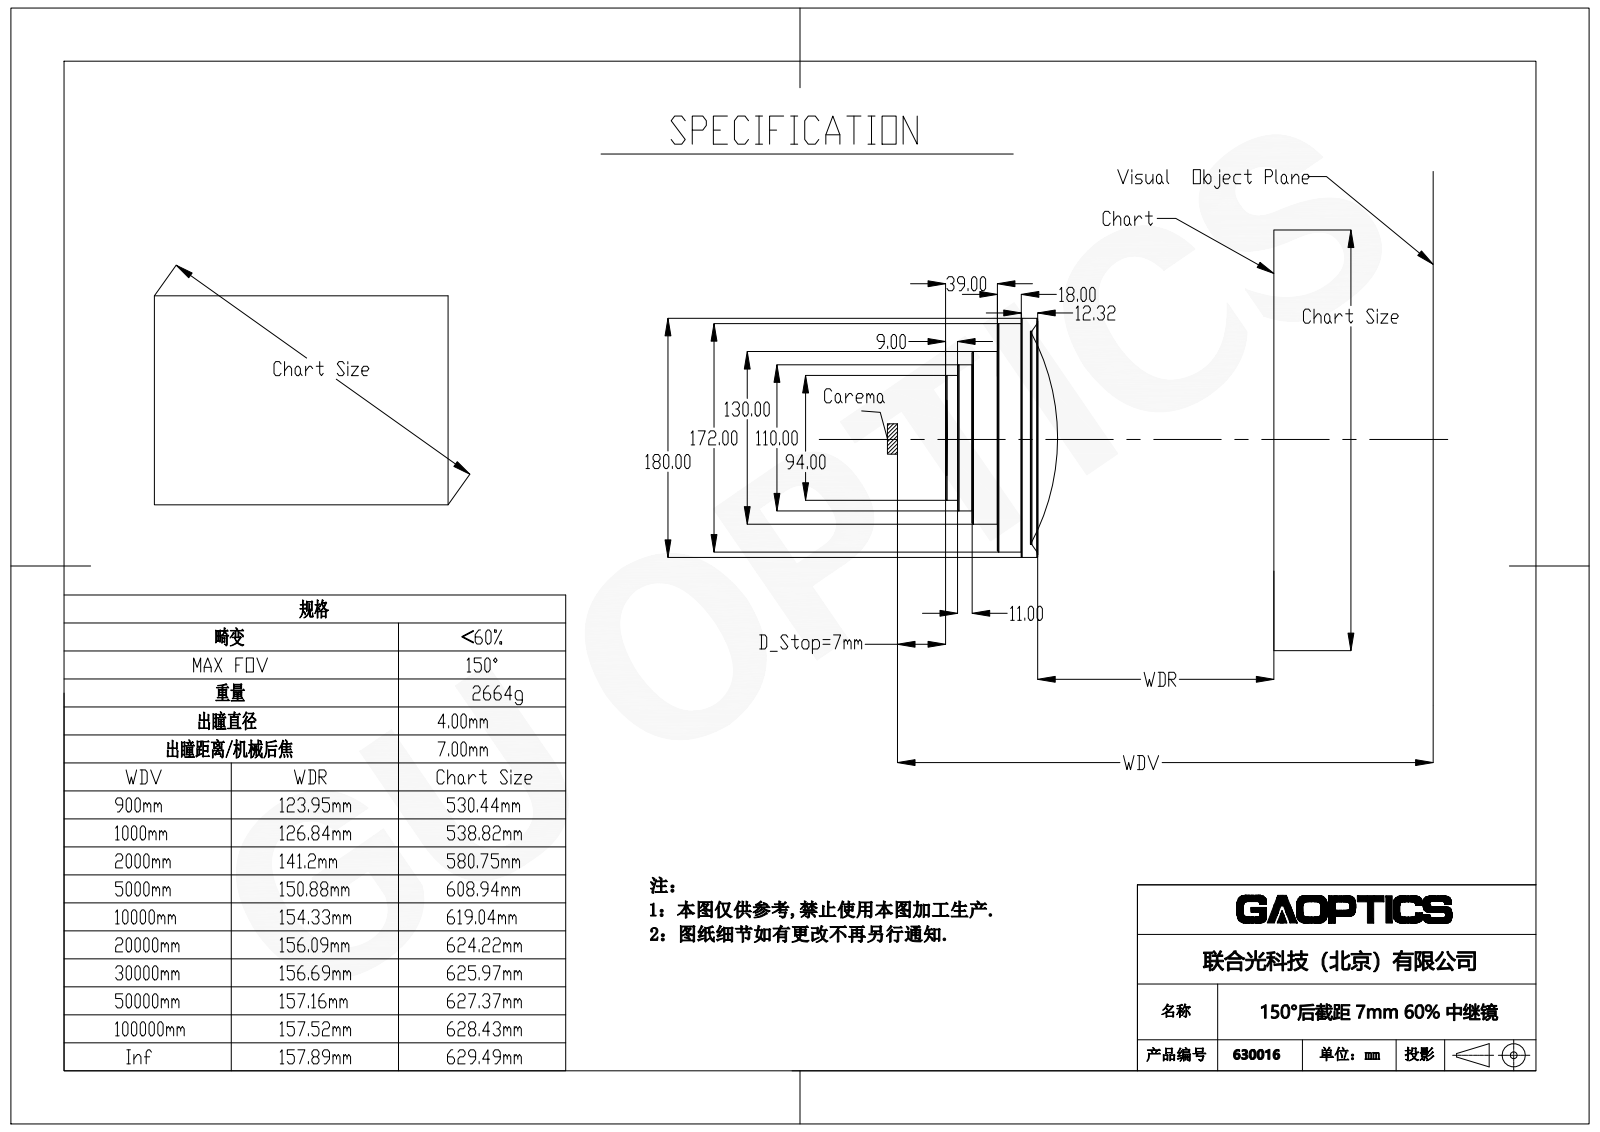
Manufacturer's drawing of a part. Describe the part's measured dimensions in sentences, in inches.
The part is named "630016". Its 3-D file was written by "SolidWorks 2020 (CONFIG_CONTROL_DESIGN)". It is 1 solid with 41 faces: 7 planar, 14 cylindrical and 20 other. Overall it measures 7.087 by 7.087 by 3.32 inches. Its volume is 75.73 cubic inches and its surface area 129 square inches. Round holes: 1 of diameter 2.226, 1 of diameter 6.319. Round bosses or shafts: 1 of diameter 7.087, 1 of diameter 6.772, 1 of diameter 5.118, 1 of diameter 4.331, 1 of diameter 3.701. The main face-to-face distances are 1.535, 0.787, 0.748, 0.354, 0.433, 1.181, 2.244, 1.89, 1.457, 0.709.
